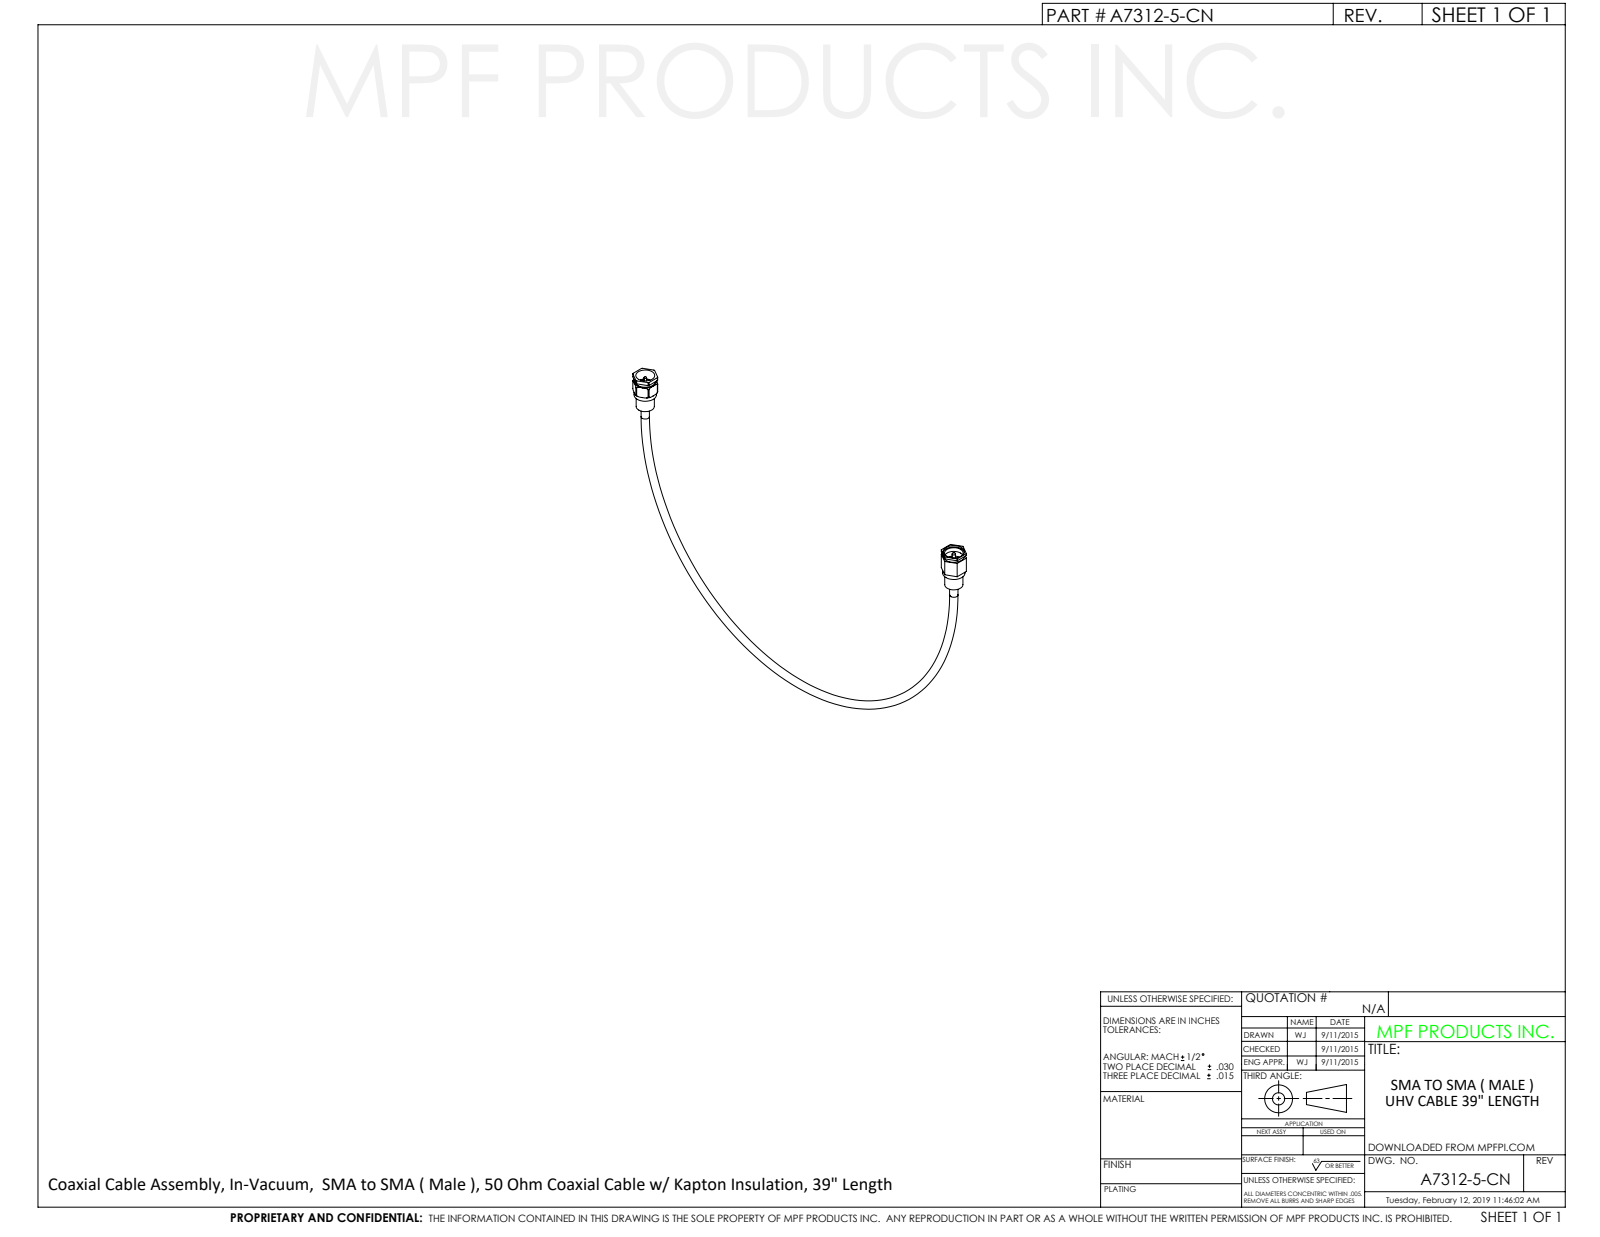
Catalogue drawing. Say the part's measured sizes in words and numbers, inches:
The part is named "A7311-5-CN". Its 3-D file was written by "SolidWorks 2012 (CONFIG_CONTROL_DESIGN)". It is 4 solids with 167 faces: 65 planar, 82 cylindrical and 20 other. Overall it measures 6.31 by 3.785 by 0.356 inches. Its volume is 0.149 cubic inches and its surface area 6.642 square inches. Round holes: 2 of diameter 0.05, 2 of diameter 0.115, 2 of diameter 0.167, 1 of diameter 0.186, 1 of diameter 0.257, 1 of diameter 0.26, 1 of diameter 0.292, 1 of diameter 0.293. Round bosses or shafts: 2 of diameter 0.25, 2 of diameter 0.18, 2 of diameter 0.165, 1 of diameter 0.307, 1 of diameter 0.307, 1 of diameter 0.294, 1 of diameter 0.278, 1 of diameter 0.207. Partial cylindrical surfaces (rounded edges, fillets, slot ends): 1 of radius 0.175. The main face-to-face distances are 0.308, 0.31, 2.691, 2.999, 3.002, 3.309, 0.274, 0.4, 0.326, 0.103. The hole center spacings are 6, 6.001.
